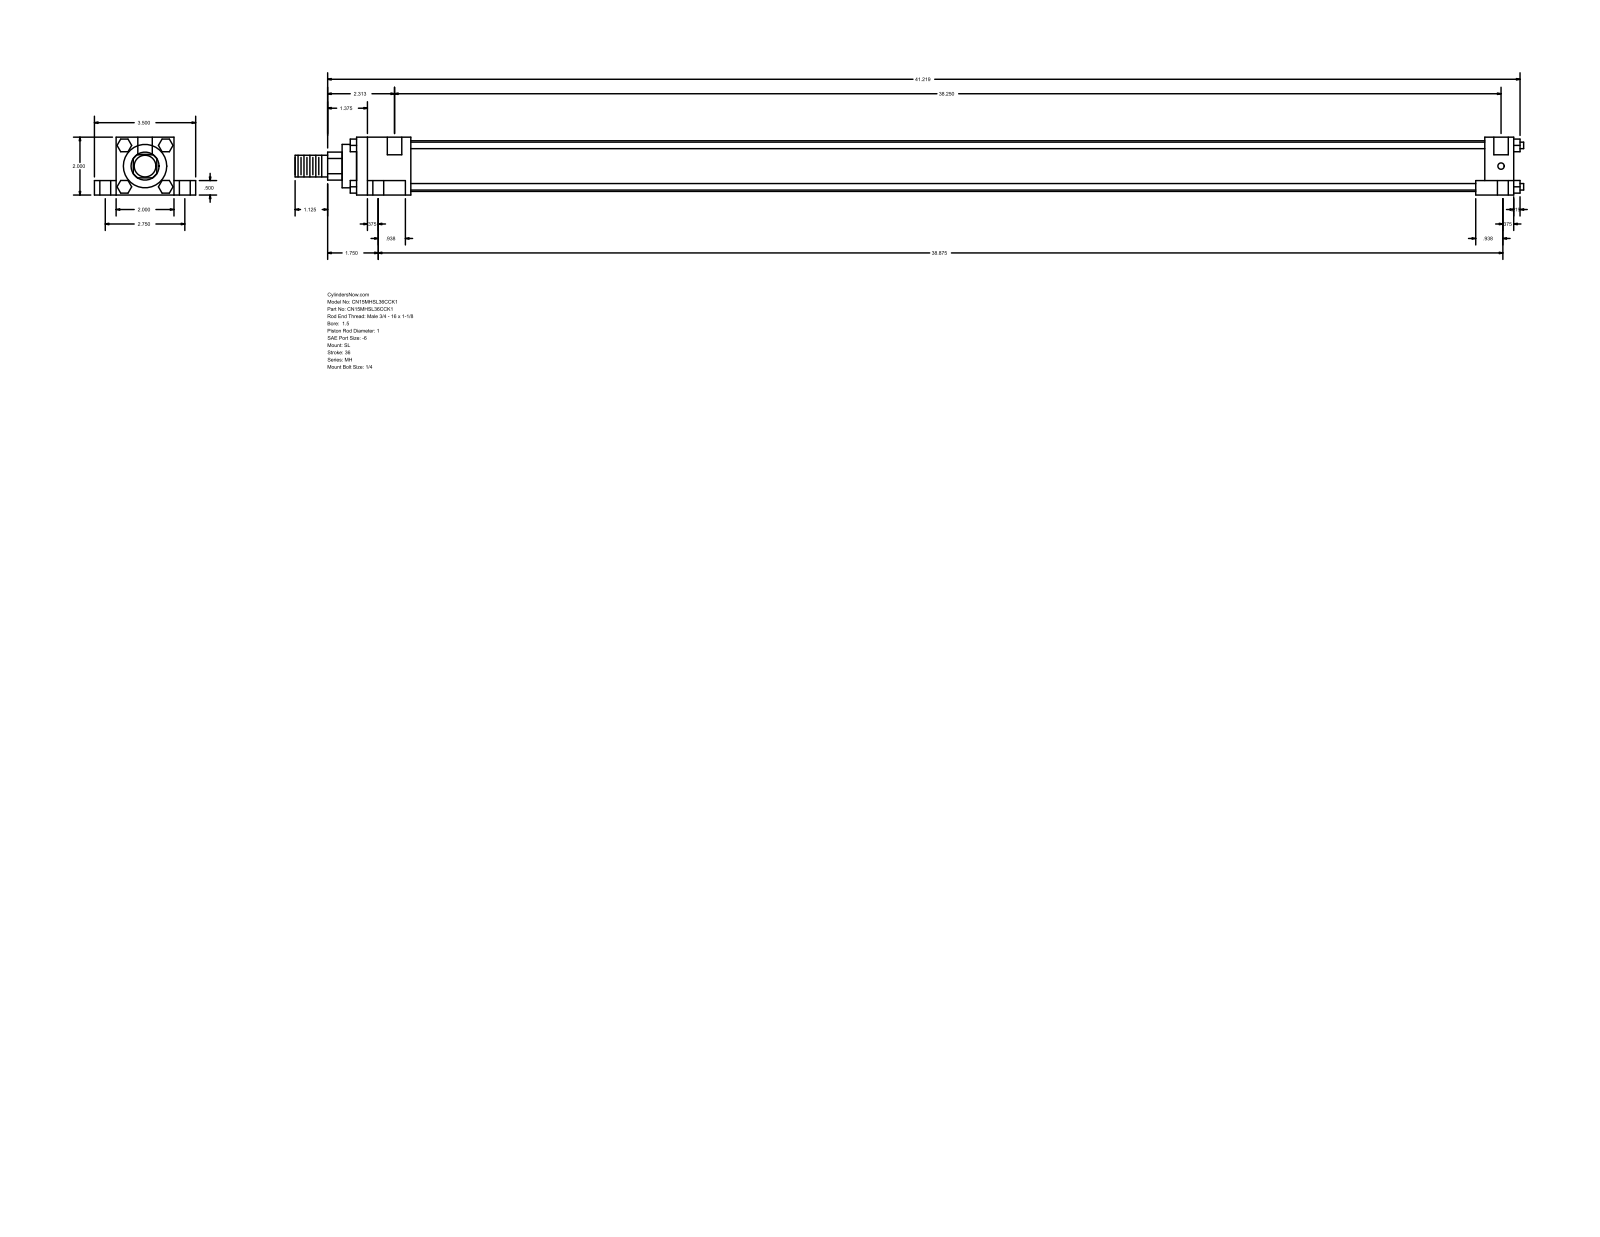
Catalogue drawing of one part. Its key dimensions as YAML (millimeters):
part_name: "MH_SL__0150_1"
step_written_by: "GSSL Pune (CONFIG_CONTROL_DESIGN)"
units: millimeters
bodies: {solids: 0, faces: 148, planar: 112, cylindrical: 36, other: 0}
overall_size: [1078.71, 88.9, 50.8]
round_holes:
  - {diameter: 5.56, count: 4}
  - {diameter: 9.53, count: 4}
  - {diameter: 15.88, count: 4}
  - {diameter: 12.7, count: 2}
round_bosses_or_shafts:
  - {diameter: 5.71, count: 4}
  - {diameter: 44.45, count: 1}
  - {diameter: 38.1, count: 1}
  - {diameter: 25.4, count: 1}
  - {diameter: 19.05, count: 1}
partial_cylinders:
  - {radius: 12.29, count: 1}
face_to_face_distances: [50.8, 12.7, 38.1, 19.05, 69.85, 1016, 25.4, 9.52, 33.34, 973.14]
hole_center_spacings: [34.96, 36.64, 37.73, 69.84, 973.77, 974.73, 976.94, 986.46]
